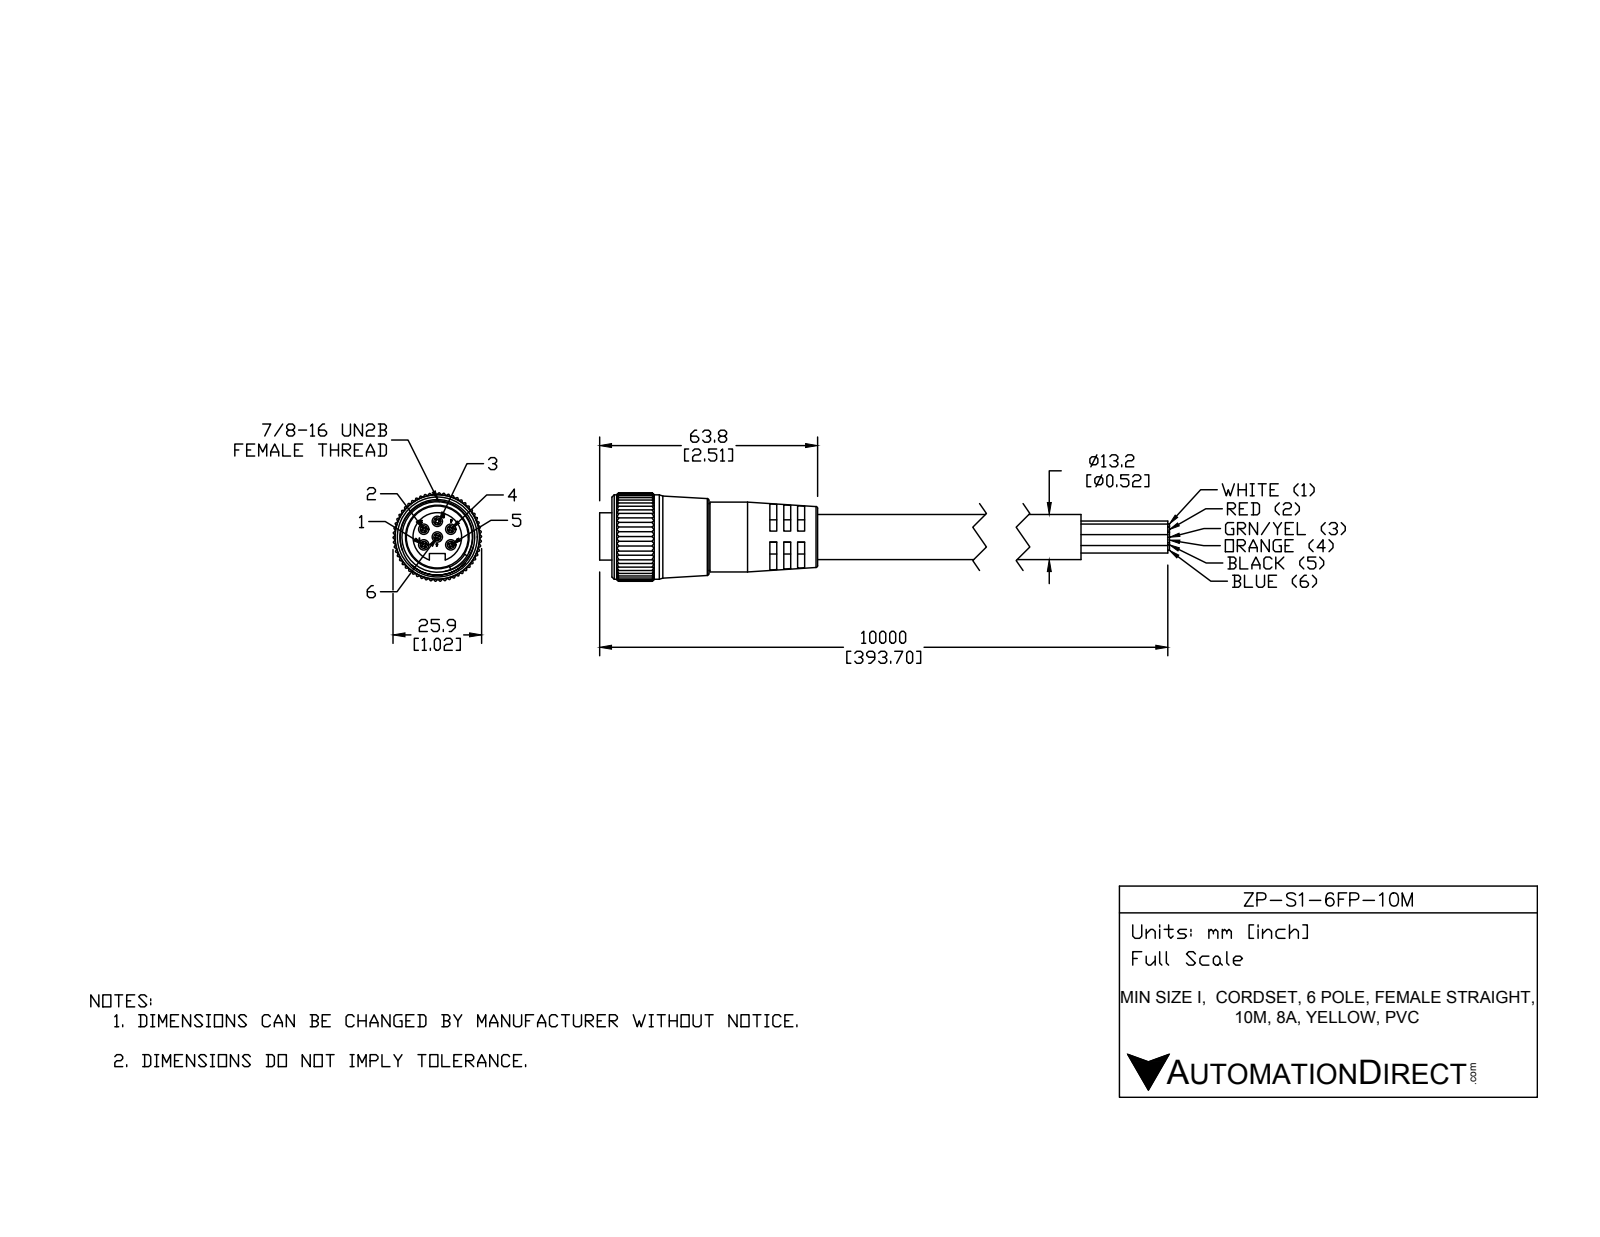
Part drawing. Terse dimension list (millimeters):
name: ZP-S1-6FP-10M
written by: SolidWorks 2015 (AUTOMOTIVE_DESIGN)
unit: mm
bodies: 2 solids, 593 faces (222 planar, 312 cylindrical, 59 other)
size: 110.36 × 52.91 × 25.84
volume: 31 008 mm³; area: 12 592 mm²
holes: 6× ⌀3.05, 1× ⌀18.14, 1× ⌀20.58, 1× ⌀21
bosses: 2× ⌀13.21, 1× ⌀24.68, 1× ⌀20.4, 1× ⌀19.5, 1× ⌀14.22
rounds: 165× R0.25, 1× R5.25, 1× R12.93
face distances: 4.03, 2, 2.03, 6.03, 8.06, 6.06, 21.13, 23.13, 25.16, 27.16
hole spacings: 4.57, 7.92, 4.58, 9.15
